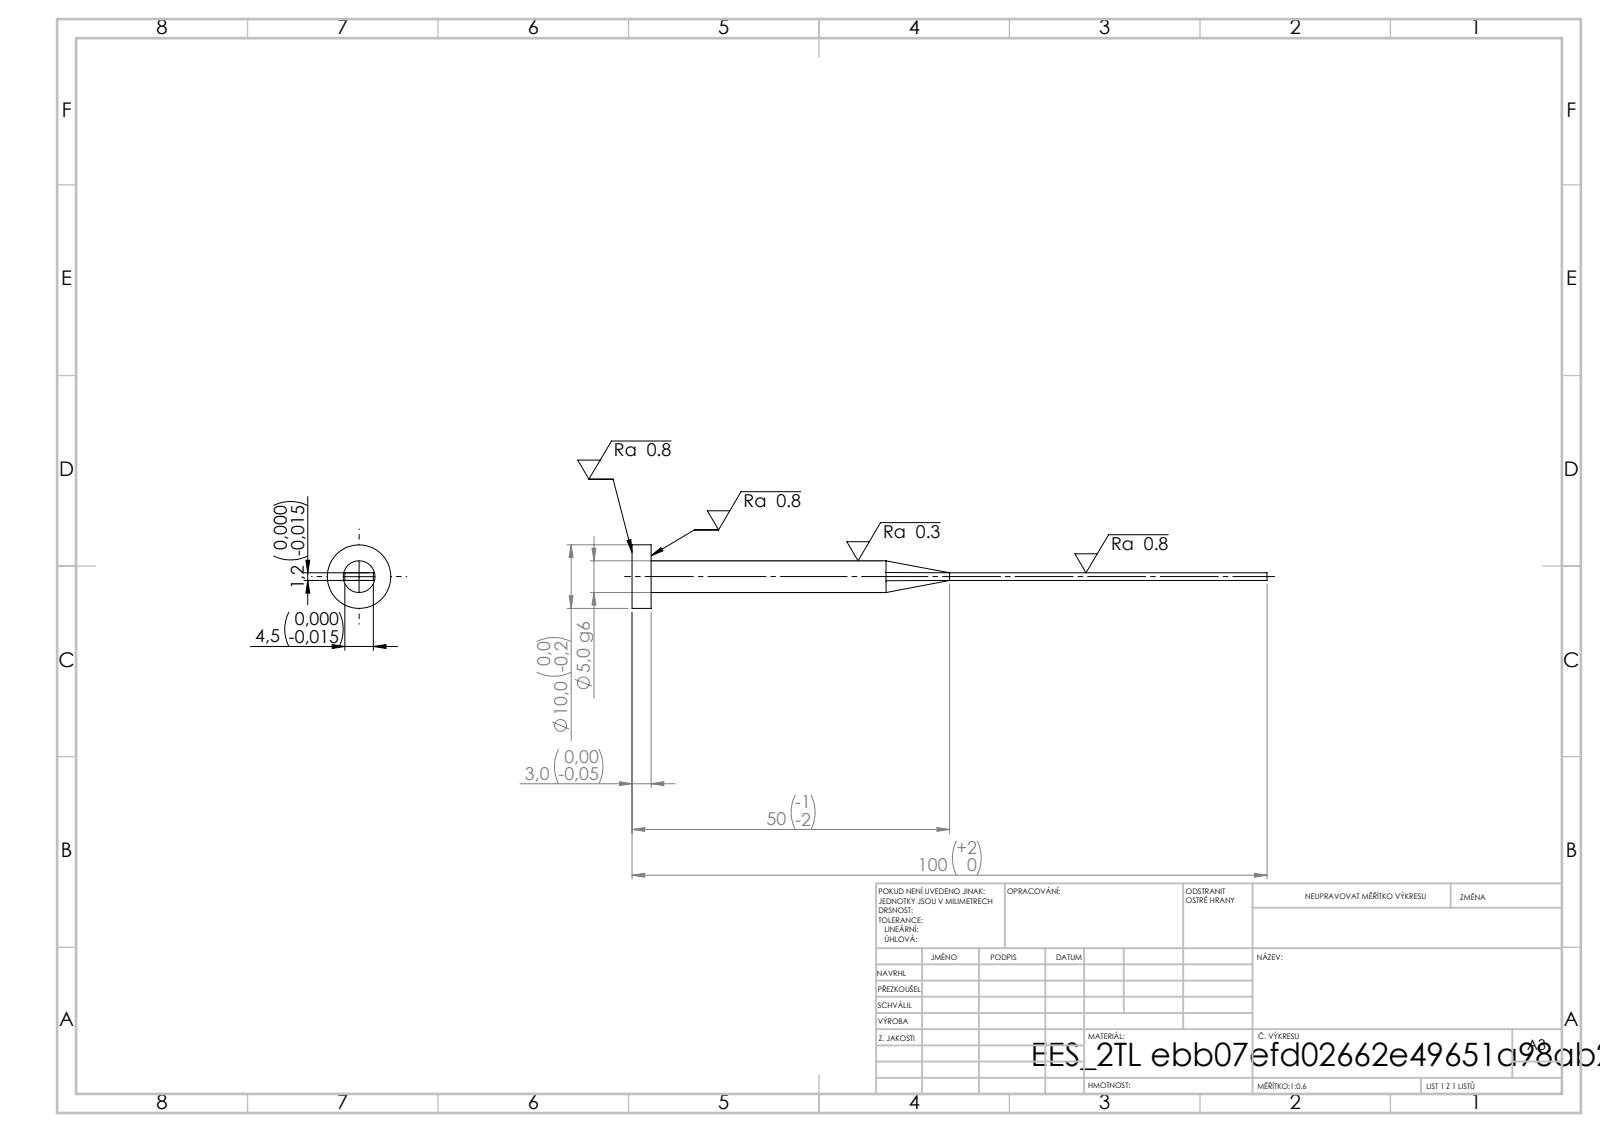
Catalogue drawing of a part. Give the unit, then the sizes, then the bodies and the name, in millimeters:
Units: millimetres
Overall size (bounding box): 100 × 10 × 10
Round bosses / shafts (diameter × count): ⌀10 ×1, ⌀5 ×1
Main face-to-face distances: 1.2, 4.5, 3, 100, 97
Volume: 1 352 mm³ · Surface area: 1 520 mm²
Bodies: 1 solid, 15 faces (7 planar, 4 cylindrical, 4 other)
STEP written by: SolidWorks 2019 (CONFIG_CONTROL_DESIGN)
